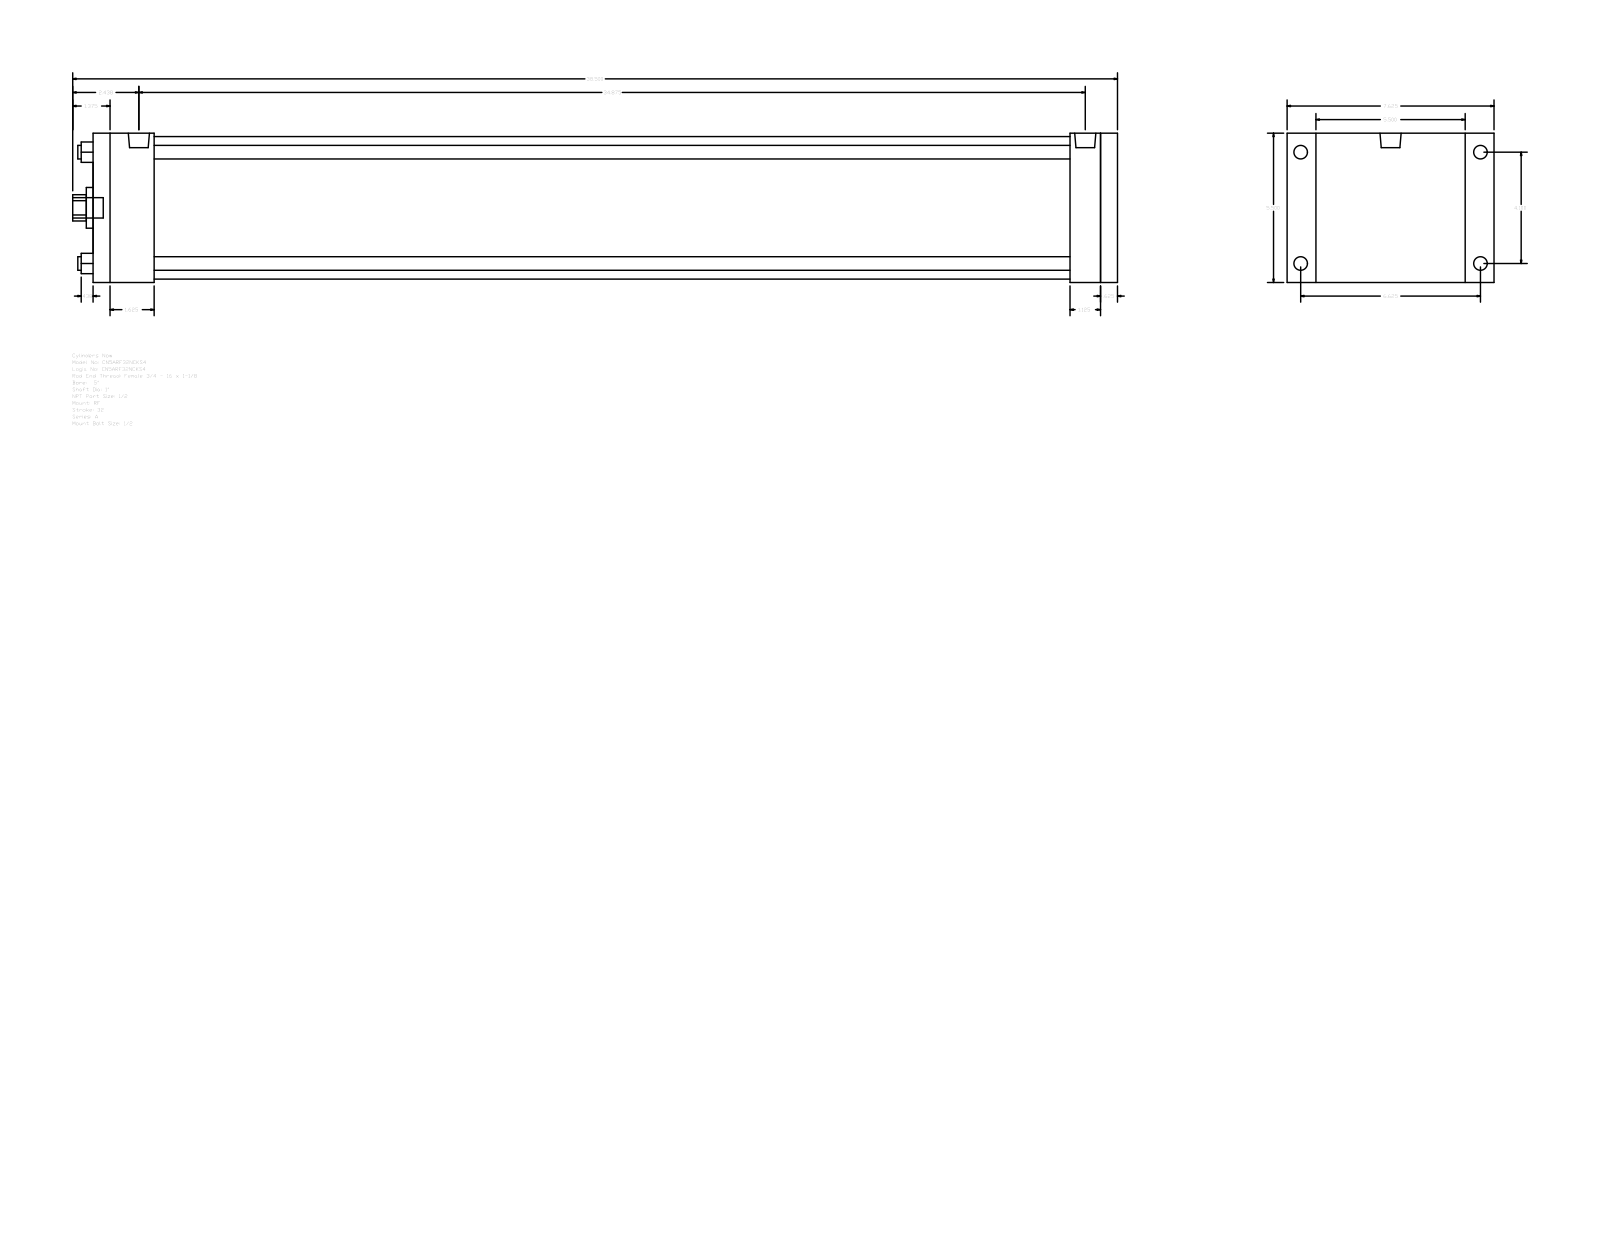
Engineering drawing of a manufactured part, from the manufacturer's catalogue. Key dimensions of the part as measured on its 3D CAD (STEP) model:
Part name (STEP PRODUCT): A_RF__0500_1
STEP written by: GSSL Pune (CONFIG_CONTROL_DESIGN)
Units: millimetres
Bodies: 0 solids, 92 faces (64 planar, 28 cylindrical, 0 other)
Overall size (bounding box): 977.9 × 193.68 × 139.7
Round holes (diameter × count): ⌀12.7 ×4, ⌀25.4 ×1, ⌀38.1 ×1, ⌀133.35 ×1
Round bosses / shafts (diameter × count): ⌀12.7 ×4, ⌀8.73 ×4, ⌀19.77 ×2, ⌀19.05 ×1
Partial cylindrical surfaces — rounded edges, fillets, slot ends (radius × count): R12.29 ×1
Main face-to-face distances: 139.7, 958.85, 942.97, 15.88, 28.57, 57.15, 885.82, 901.7, 914.4, 857.25
Hole centre spacings: 73.64, 104.14, 147.28
